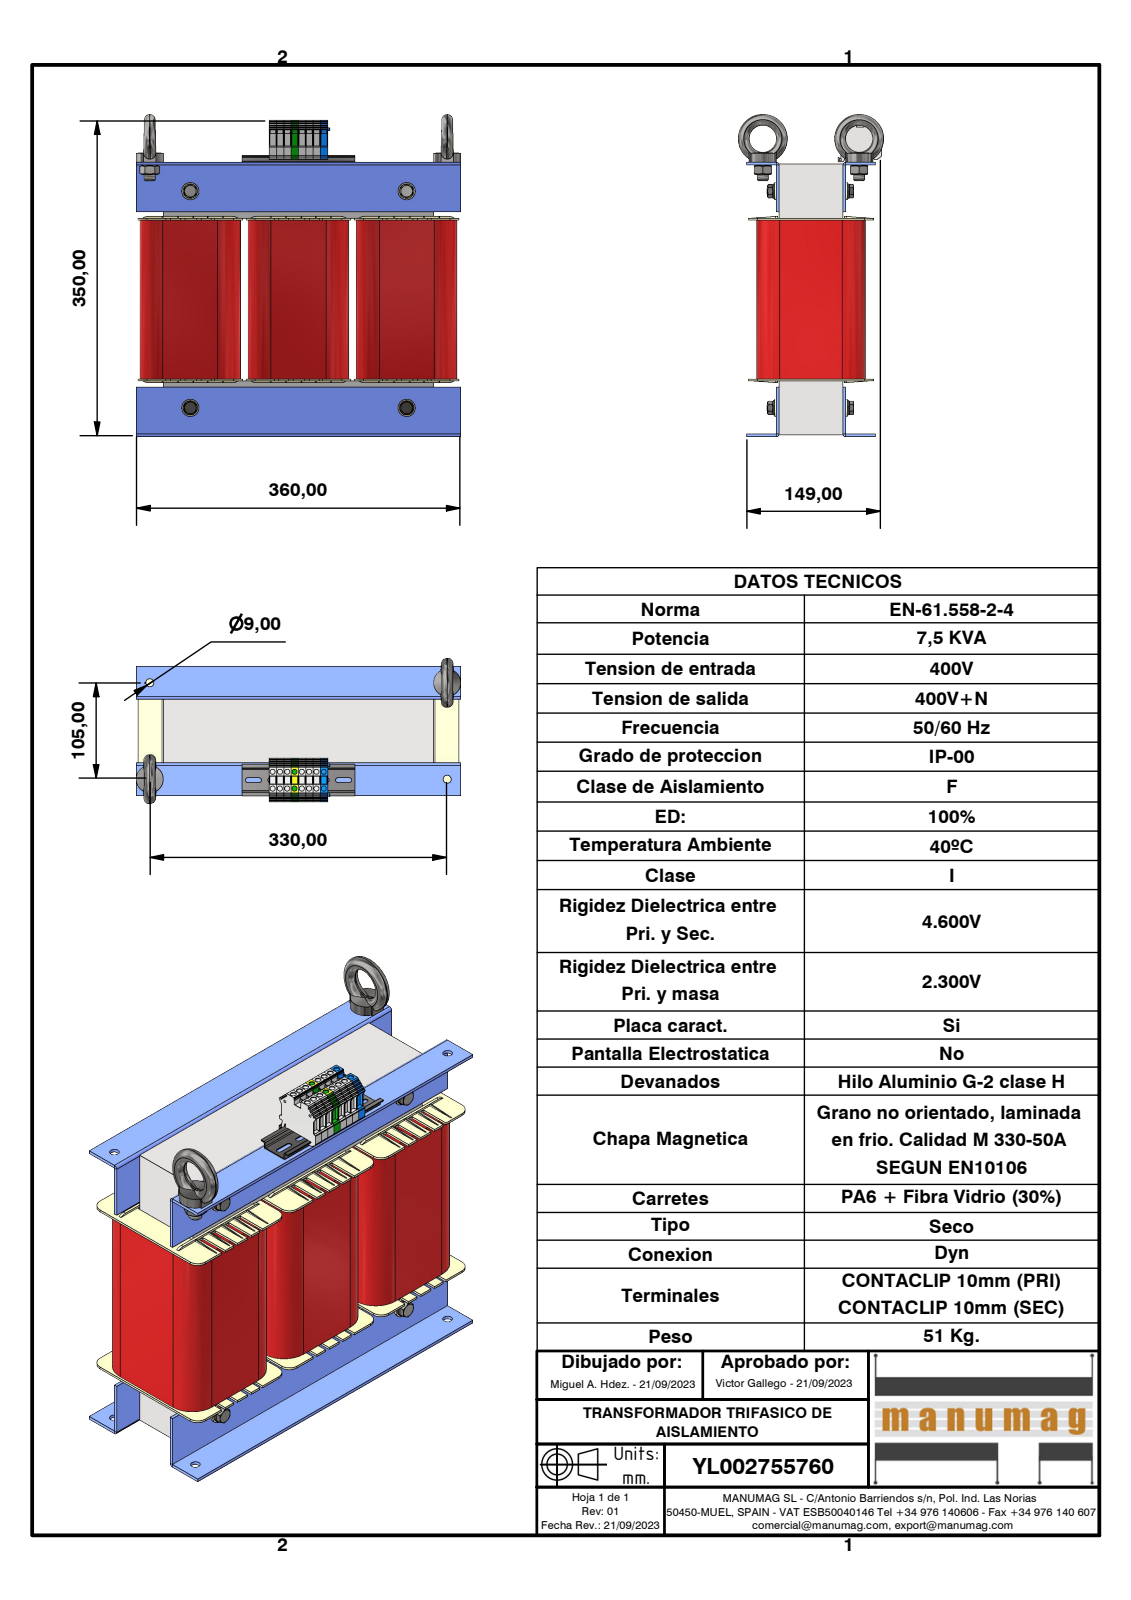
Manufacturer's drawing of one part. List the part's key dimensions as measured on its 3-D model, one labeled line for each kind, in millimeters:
Part name (STEP PRODUCT): YL002755760; UI 180 - 70 (300x300); UI 180_70_BOBINADO; RC60 NT060 (+8 more)
STEP written by: Autodesk Inventor 2023 (AUTOMOTIVE_DESIGN)
Units: millimetres
Bodies: 45 solids, 3384 faces (2398 planar, 798 cylindrical, 188 other)
Overall size (bounding box): 360 × 357 × 160
Volume: 9 674 000 mm³ · Surface area: 1 432 000 mm²
Round holes (diameter × count): ⌀5.7 ×16, ⌀6.65 ×4, ⌀8 ×4, ⌀8.4 ×4, ⌀9 ×4, ⌀10.5 ×4, ⌀11 ×4, ⌀2.4 ×2, ⌀2.5 ×2, ⌀2.75 ×2, ⌀10.11 ×2, ⌀30 ×2
Round bosses / shafts (diameter × count): ⌀19 ×4, ⌀16 ×4, ⌀11.4 ×4, ⌀9.6 ×4, ⌀7.32 ×4, ⌀54 ×2, ⌀12 ×2, ⌀10.8 ×2
Partial cylindrical surfaces — rounded edges, fillets, slot ends (radius × count): R0.3 ×81, R1 ×28, R10 ×24, R2 ×17, R3 ×12, R3.31 ×12, R25.37 ×12, R2.6 ×10
Main face-to-face distances: 2.5, 1, 240, 1.5, 3, 73, 60, 70, 120, 22.06
Hole centre spacings: 8.1, 20.1, 16.2, 24.52, 24.3, 30.48, 18.4, 32.4
